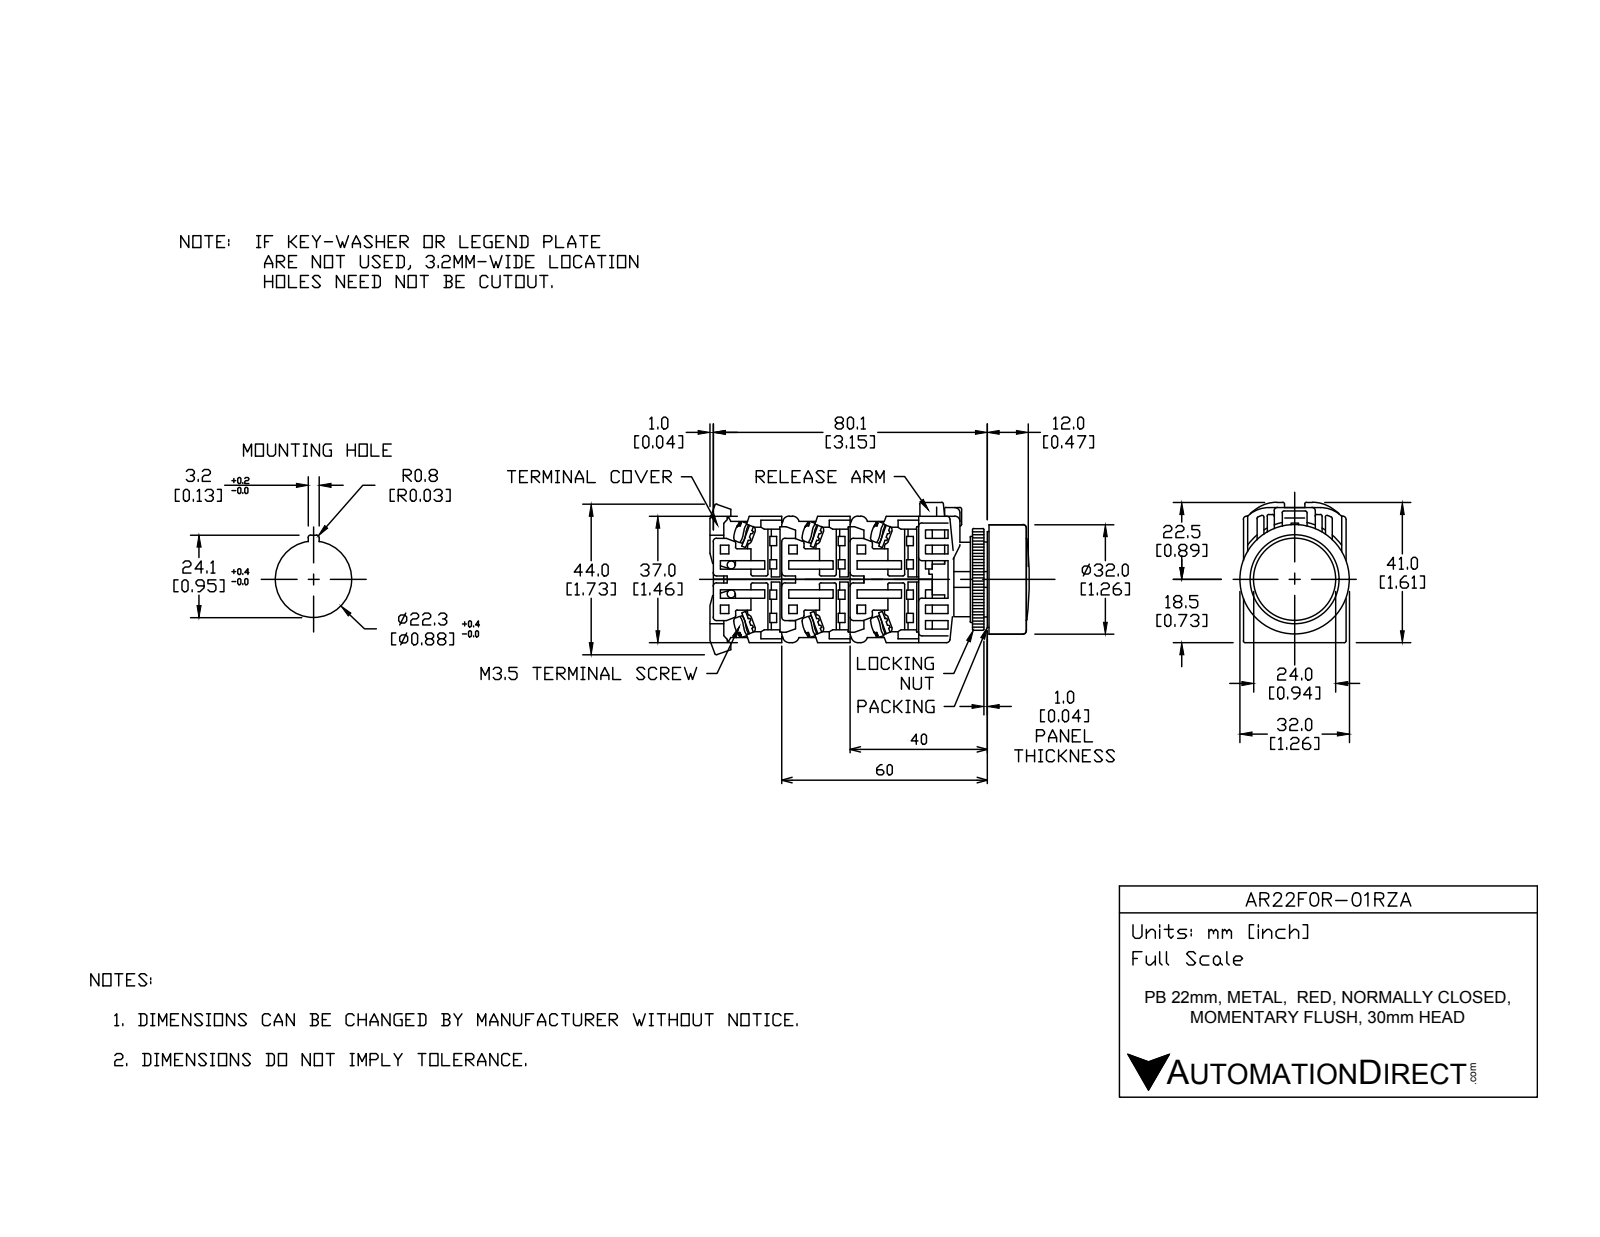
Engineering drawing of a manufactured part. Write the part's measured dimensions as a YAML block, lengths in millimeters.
part_name: "AR22F0R-01RZA"
step_written_by: "SolidWorks 2017 (AUTOMOTIVE_DESIGN)"
units: millimeters
bodies: {solids: 12, faces: 295, planar: 201, cylindrical: 74, other: 20}
overall_size: [52.75, 41, 32]
volume: 27343
surface_area: 19391
round_holes:
  - {diameter: 21.8, count: 1}
  - {diameter: 22, count: 1}
  - {diameter: 25, count: 1}
  - {diameter: 31, count: 1}
round_bosses_or_shafts:
  - {diameter: 5, count: 2}
  - {diameter: 32, count: 1}
  - {diameter: 30.5, count: 1}
  - {diameter: 29.8, count: 1}
  - {diameter: 24, count: 1}
  - {diameter: 23.8, count: 1}
  - {diameter: 21.75, count: 1}
  - {diameter: 17, count: 1}
partial_cylinders:
  - {radius: 0.5, count: 23}
  - {radius: 1.75, count: 4}
  - {radius: 5, count: 4}
  - {radius: 4, count: 2}
  - {radius: 16.59, count: 1}
  - {radius: 17.59, count: 1}
face_to_face_distances: [1, 28.5, 18, 3, 2, 29, 30, 10.5, 8, 20.5]
